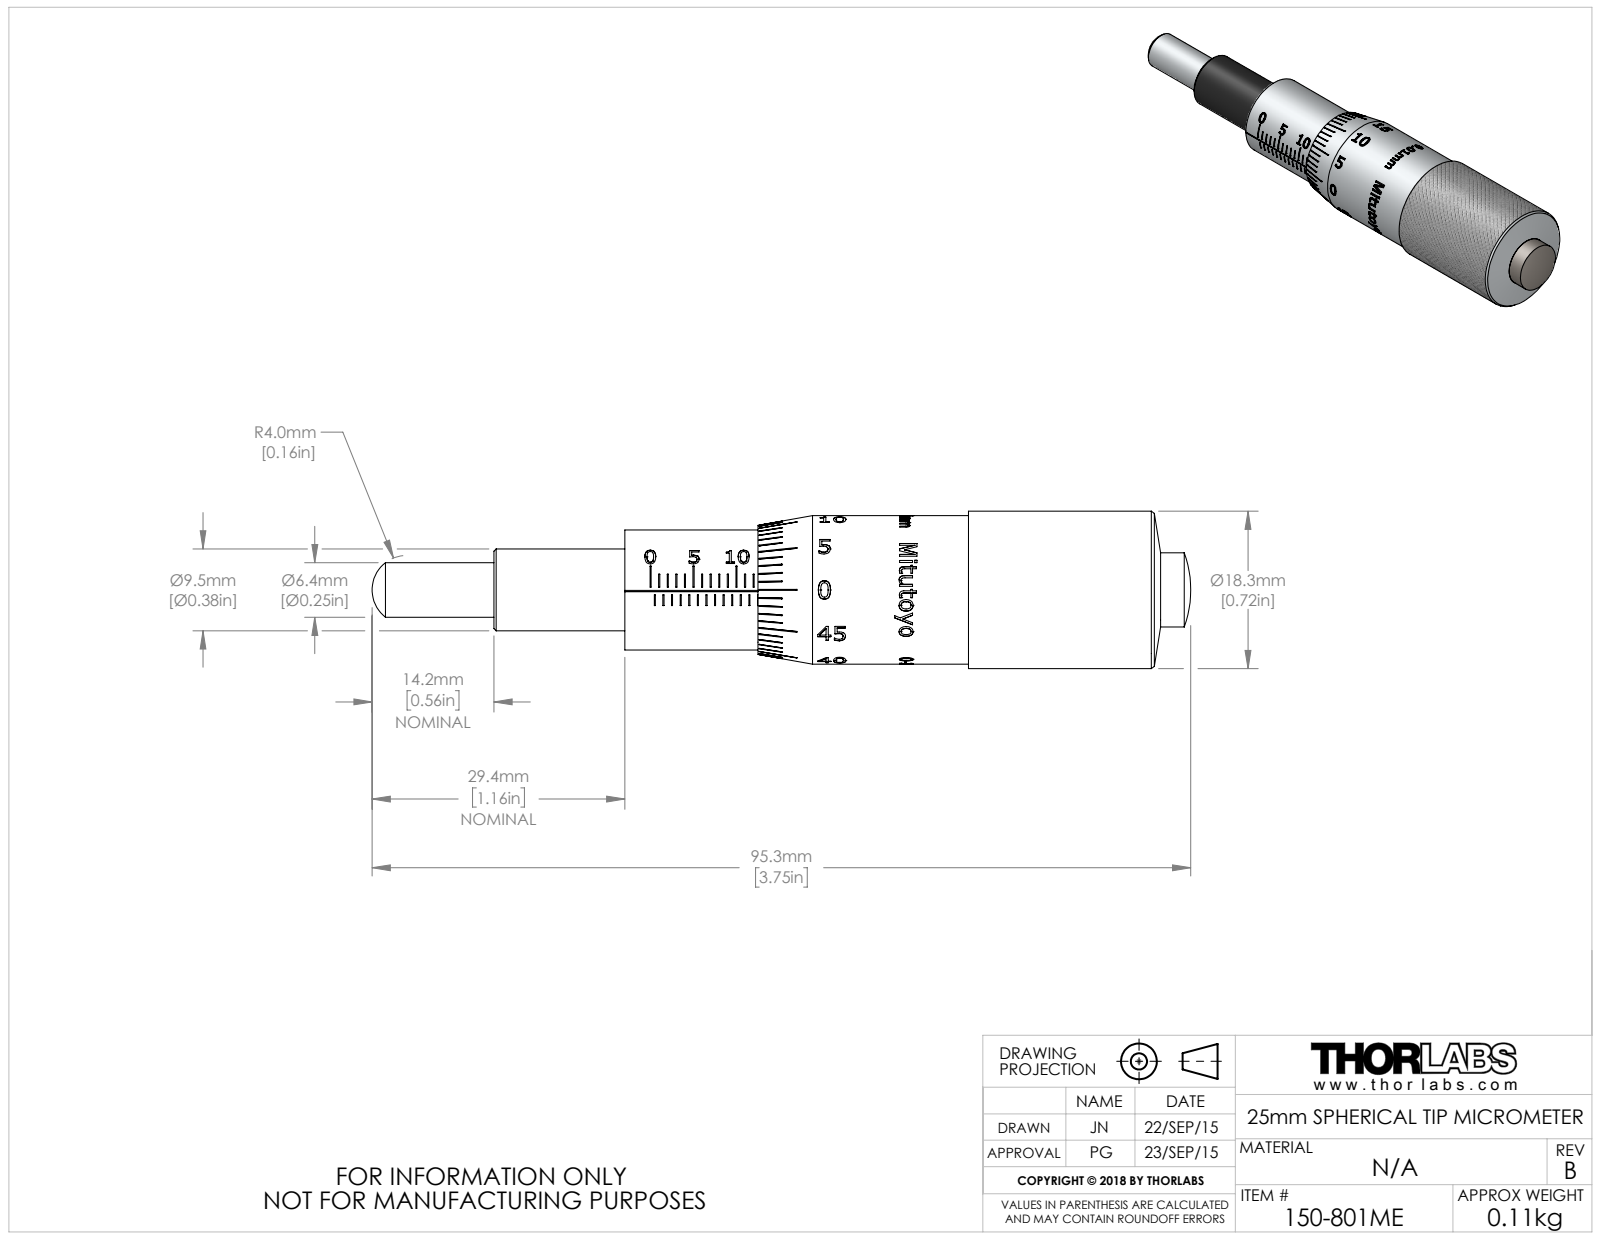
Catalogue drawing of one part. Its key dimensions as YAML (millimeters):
part_name: "TTN045981-E0W"
step_written_by: "SolidWorks 2016 (AUTOMOTIVE_DESIGN)"
units: millimeters
bodies: {solids: 3, faces: 1346, planar: 617, cylindrical: 244, other: 485}
overall_size: [95.31, 18.3, 18.3]
volume: 12946
surface_area: 10212
round_holes:
  - {diameter: 1.68, count: 1}
  - {diameter: 4, count: 1}
  - {diameter: 6.35, count: 1}
  - {diameter: 14.22, count: 1}
round_bosses_or_shafts:
  - {diameter: 18.3, count: 1}
  - {diameter: 17.27, count: 1}
  - {diameter: 13.97, count: 1}
  - {diameter: 11.18, count: 1}
  - {diameter: 9.53, count: 1}
  - {diameter: 8.61, count: 1}
  - {diameter: 3.49, count: 1}
partial_cylinders:
  - {radius: 6.97, count: 1}
  - {radius: 7.54, count: 1}
  - {radius: 8, count: 1}
  - {radius: 8.31, count: 1}
  - {radius: 8.62, count: 1}
face_to_face_distances: [8.38, 22.98, 53.97, 62.35, 39.37, 14.6, 30.99, 31.36, 15.24, 46.23]
